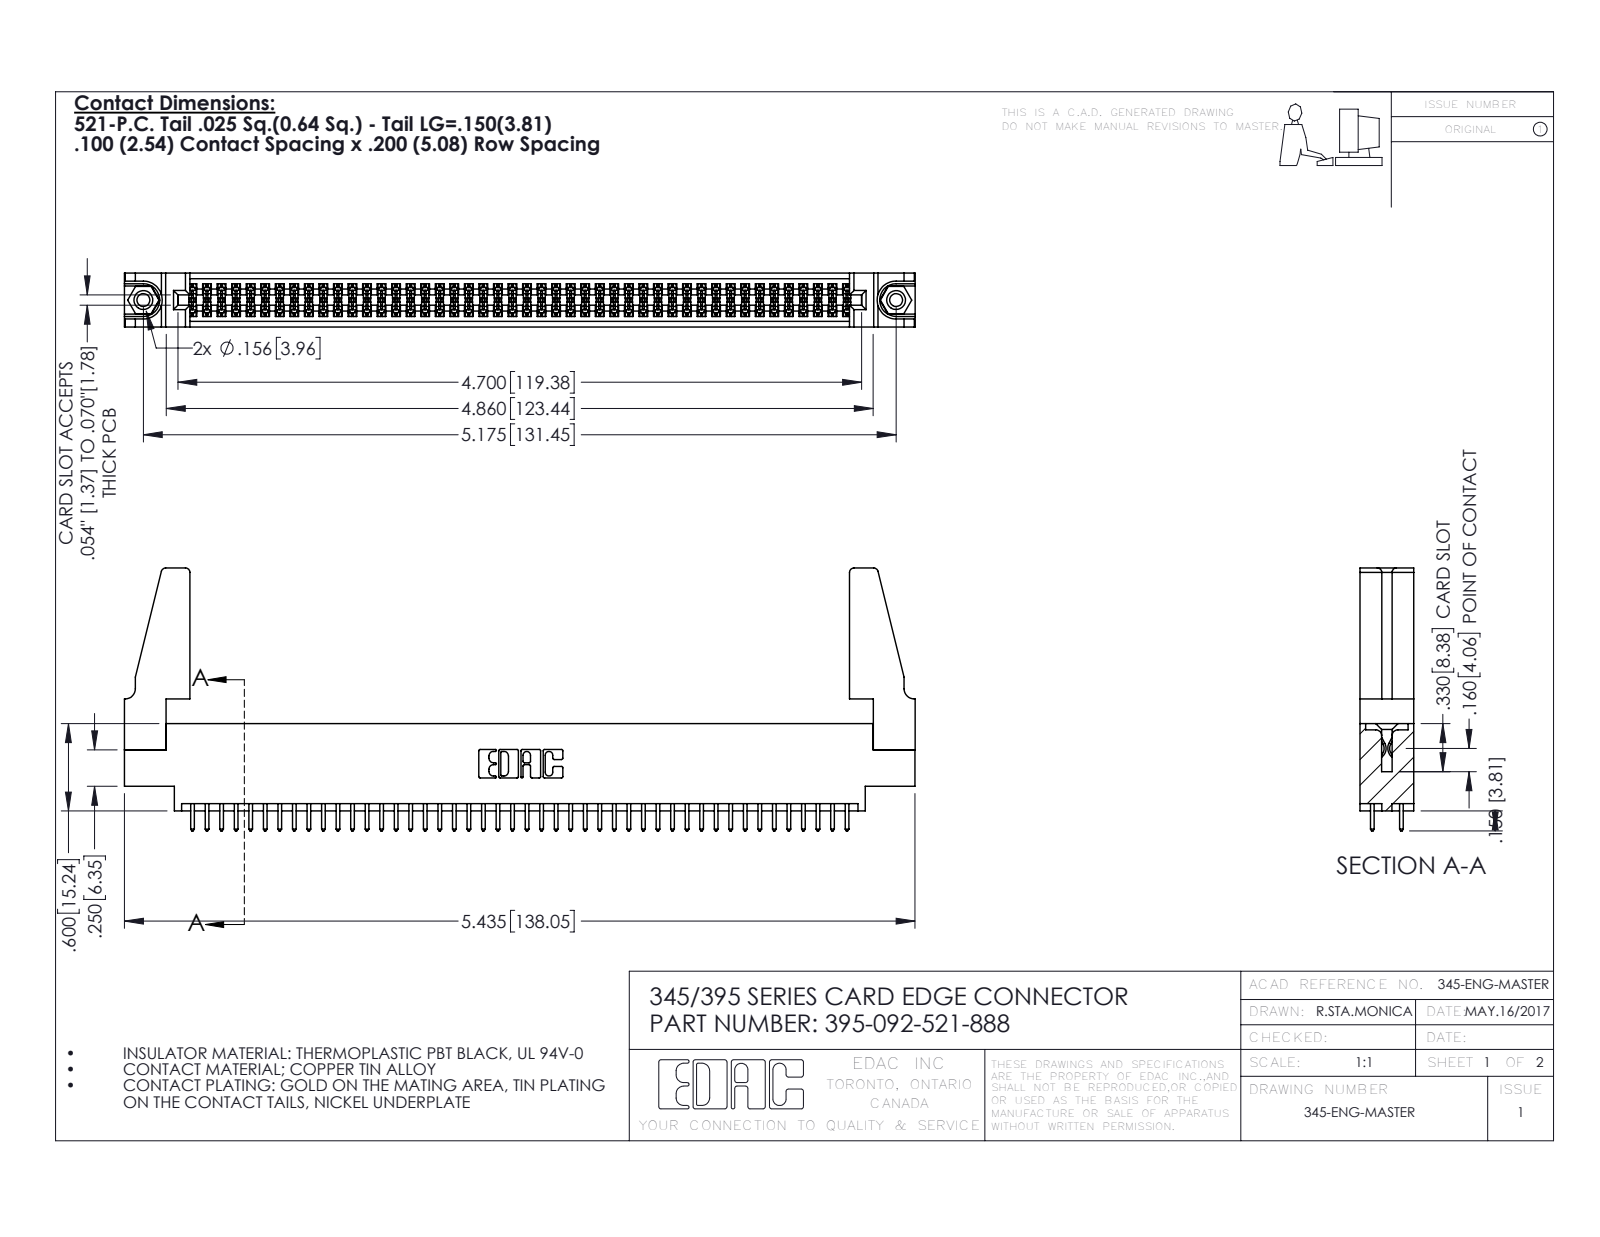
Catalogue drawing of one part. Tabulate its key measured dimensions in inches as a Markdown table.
| quantity | value |
| --- | --- |
| part name | 345 Part_0.170 Offset - 0.156 Dia-TH; 345-250-001_345-250-001-102; 395-092-521-888; 345-220-078_345-220-088 (+1 more) |
| STEP written by | SolidWorks 2016 (CONFIG_CONTROL_DESIGN) |
| units | inches |
| bodies | 97 solids, 4854 faces (3192 planar, 1646 cylindrical, 16 other) |
| overall size | 5.436 × 1.807 × 0.37 |
| volume | 1.01 in³ |
| surface area | 35.27 in² |
| round holes (diameter × count) | 0.089 × 2, 0.125 × 2, 0.156 × 2, 0.064 × 1 |
| round bosses / shafts (diameter × count) | 0.155 × 2 |
| partial cylindrical surfaces (radius × count) | 0.006 × 138, 0.01 × 92, 0.01 × 22, 0.03 × 8, 0.007 × 6, 0.031 × 6, 0.026 × 3, 0.014 × 2 |
| main face-to-face distances | 0.072, 0.298, 0.37, 0.2, 0.098, 0.272, 0.025, 0.225, 0.175, 0.149 |
| hole center spacings | 0.27, 4.939, 5.175 |
